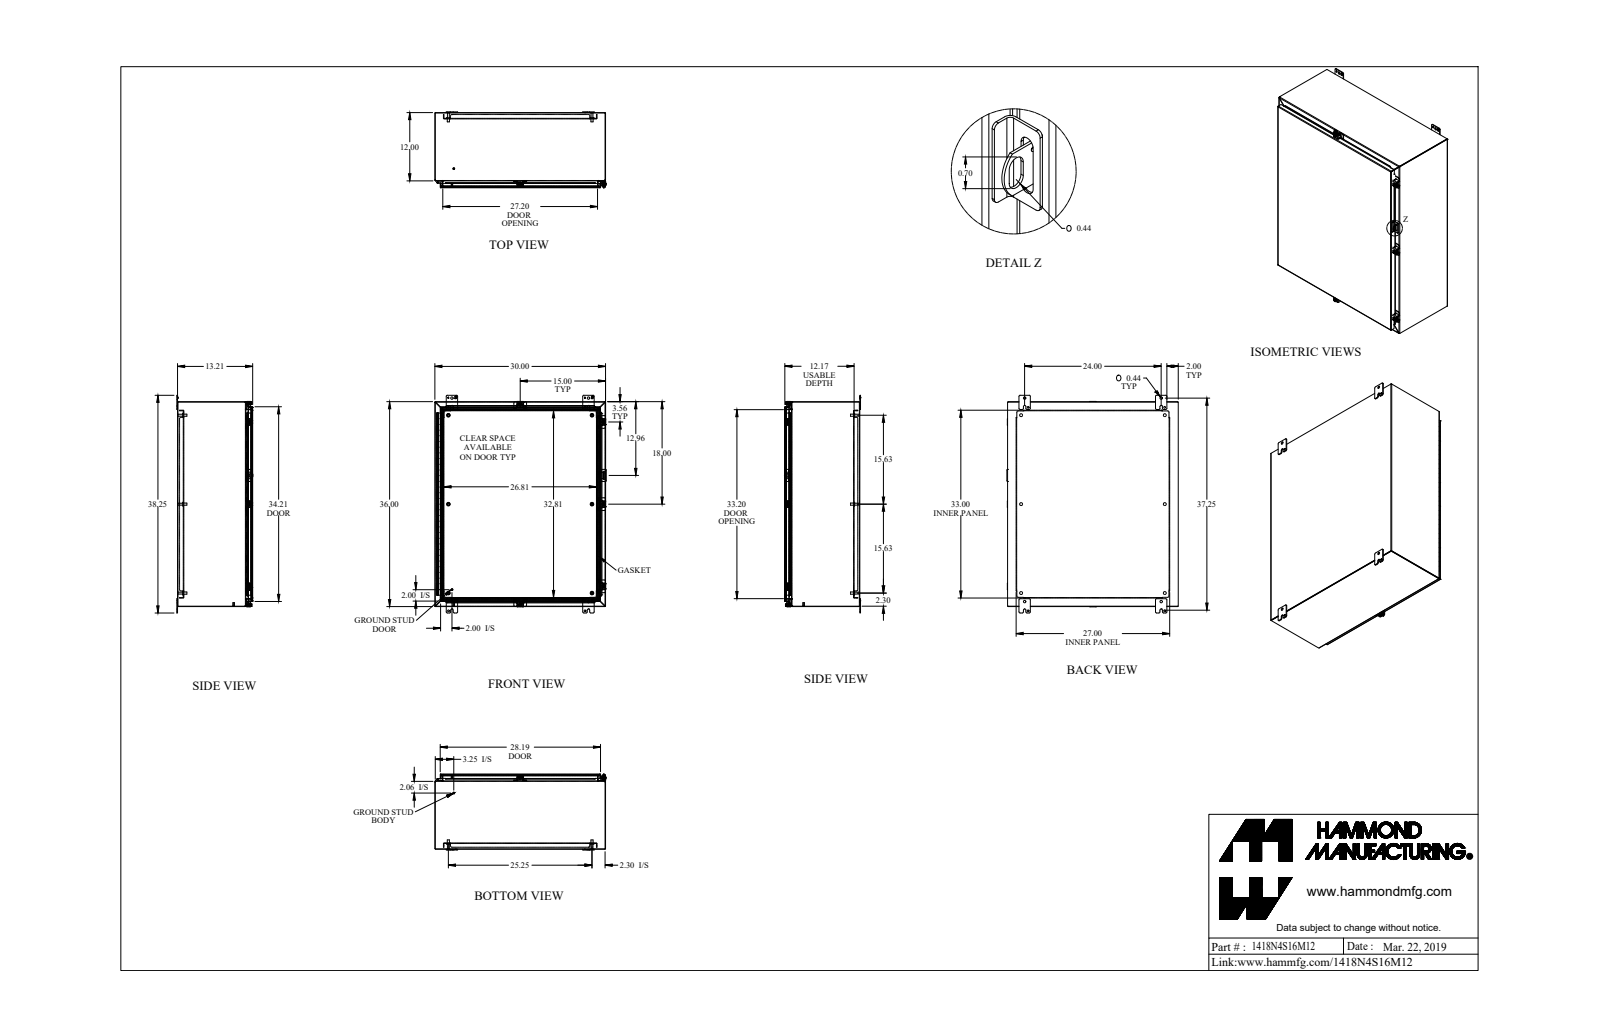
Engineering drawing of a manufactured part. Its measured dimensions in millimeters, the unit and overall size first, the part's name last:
Units: millimetres
Overall size (bounding box): 971.6 × 765.2 × 339.7
Round holes (diameter × count): ⌀12.7 ×6, ⌀5.4 ×5, ⌀6.7 ×5, ⌀7.8 ×4, ⌀8 ×4, ⌀9.5 ×4, ⌀11.1 ×4, ⌀11.3 ×2, ⌀11.3 ×2, ⌀2.8 ×1, ⌀3.2 ×1, ⌀9.5 ×1
Round bosses / shafts (diameter × count): ⌀16.5 ×6, ⌀9.5 ×6, ⌀8.4 ×6, ⌀12.7 ×5, ⌀9.9 ×5, ⌀6.2 ×5, ⌀25.4 ×4, ⌀8 ×2
Partial cylindrical surfaces — rounded edges, fillets, slot ends (radius × count): R6.4 ×36, R1.2 ×27, R3.6 ×27, R4.8 ×26, R0.9 ×22, R2.7 ×22, R3.2 ×14, R3.6 ×10
Main face-to-face distances: 1.8, 1.8, 331.9, 333.7, 333.7, 335.5, 307.5, 305.7, 26.2, 28
Hole centre spacings: 1020.5, 396.9, 641.4, 325.2, 325.2, 553.3, 609.6, 793.8
Volume: 6 597 000 mm³ · Surface area: 6 817 000 mm²
Bodies: 51 solids, 1661 faces (872 planar, 645 cylindrical, 144 other)
Part name (STEP PRODUCT): 1418N4S16M12_Default
STEP written by: SolidWorks 2019 (CONFIG_CONTROL_DESIGN)
